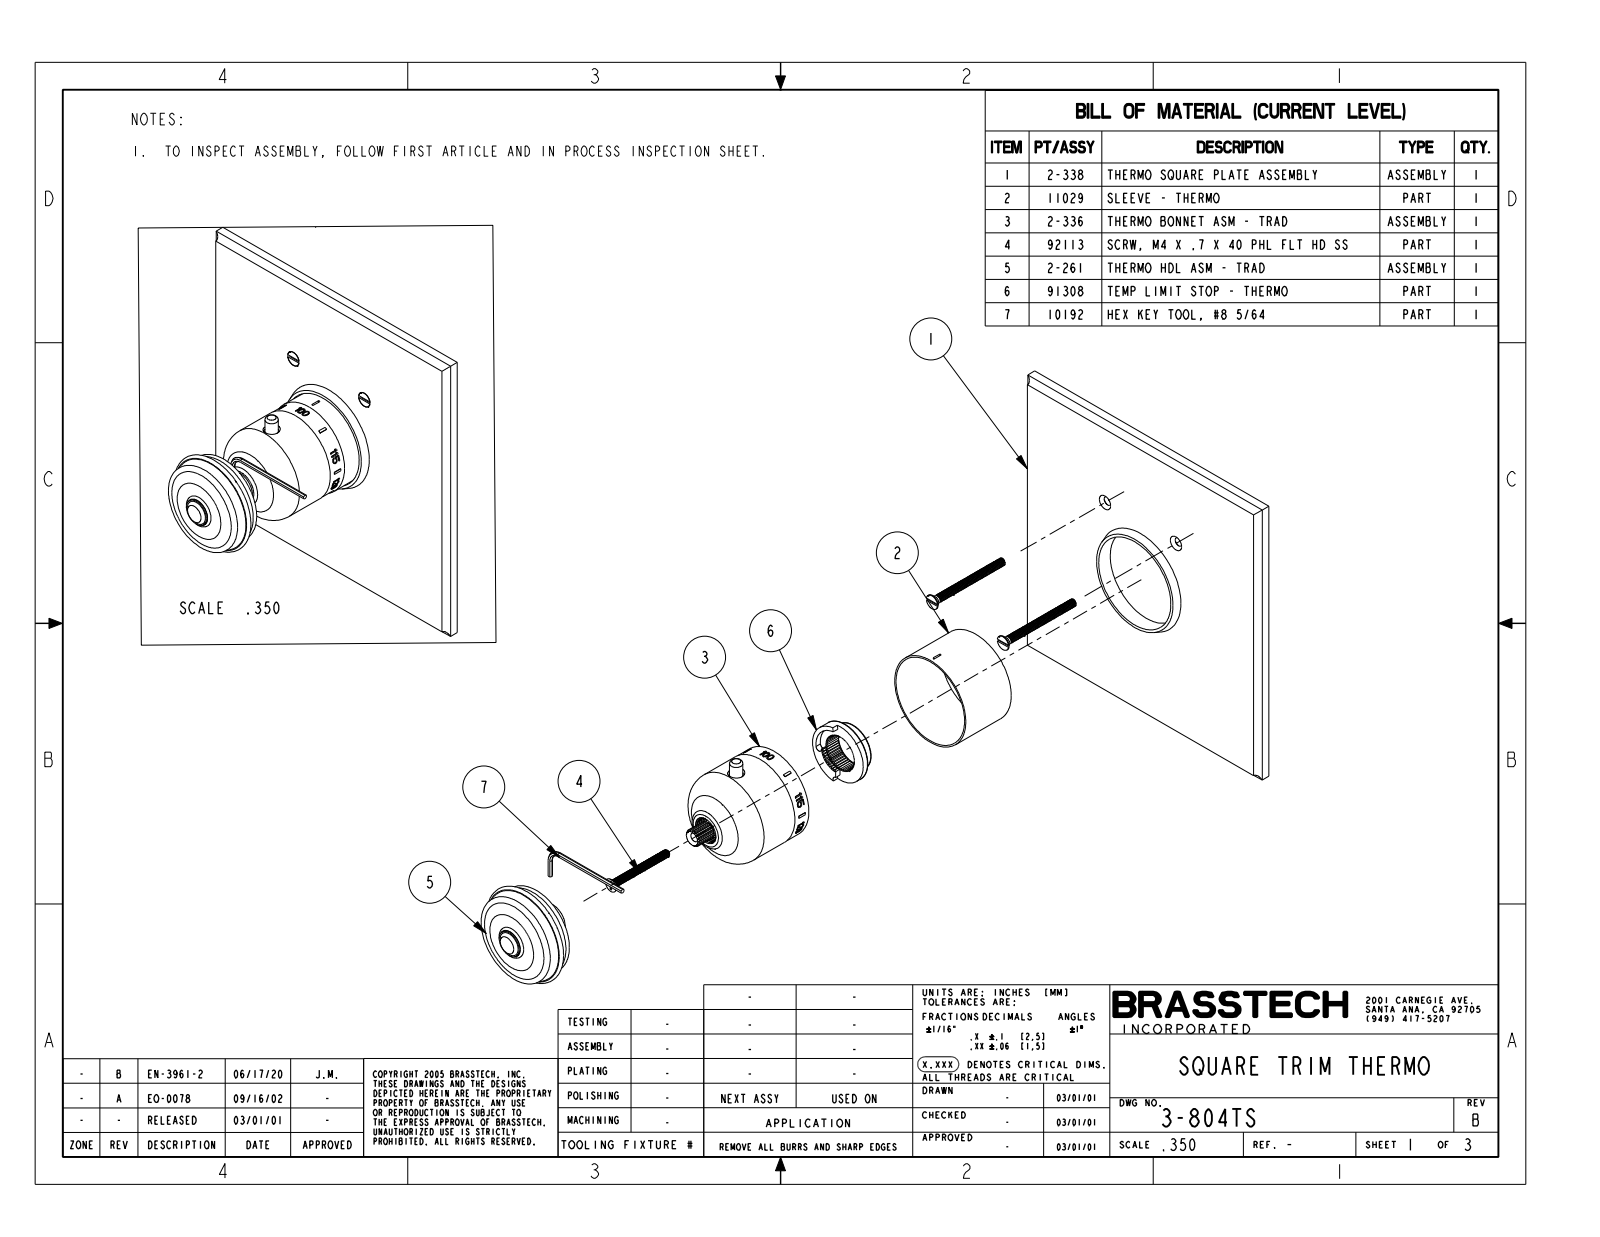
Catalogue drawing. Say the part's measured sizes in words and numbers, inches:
The part is named "3-804TS". Its 3-D file was written by "CREO PARAMETRIC BY PTC INC, 2018400 (CONFIG_CONTROL_DESIGN)". It is 1 solid with 405 faces: 338 planar, 39 cylindrical and 28 other. Overall it measures 6.5 by 6.5 by 4.046 inches. Its volume is 21.65 cubic inches and its surface area 115 square inches. Round bosses or shafts: 1 of diameter 1.97, 1 of diameter 1.94, 1 of diameter 1.929, 1 of diameter 0.69, 1 of diameter 0.55, 1 of diameter 0.37, 1 of diameter 0.26, 1 of diameter 0.067. Partial cylindrical surfaces (rounded edges, fillets, slot ends): 4 of radius 0.125, 1 of radius 0.969. The main face-to-face distances are 0.313, 6.5, 3.914, 3.601, 3.164, 2.851, 0.75, 2.745, 2.432, 0.419.
